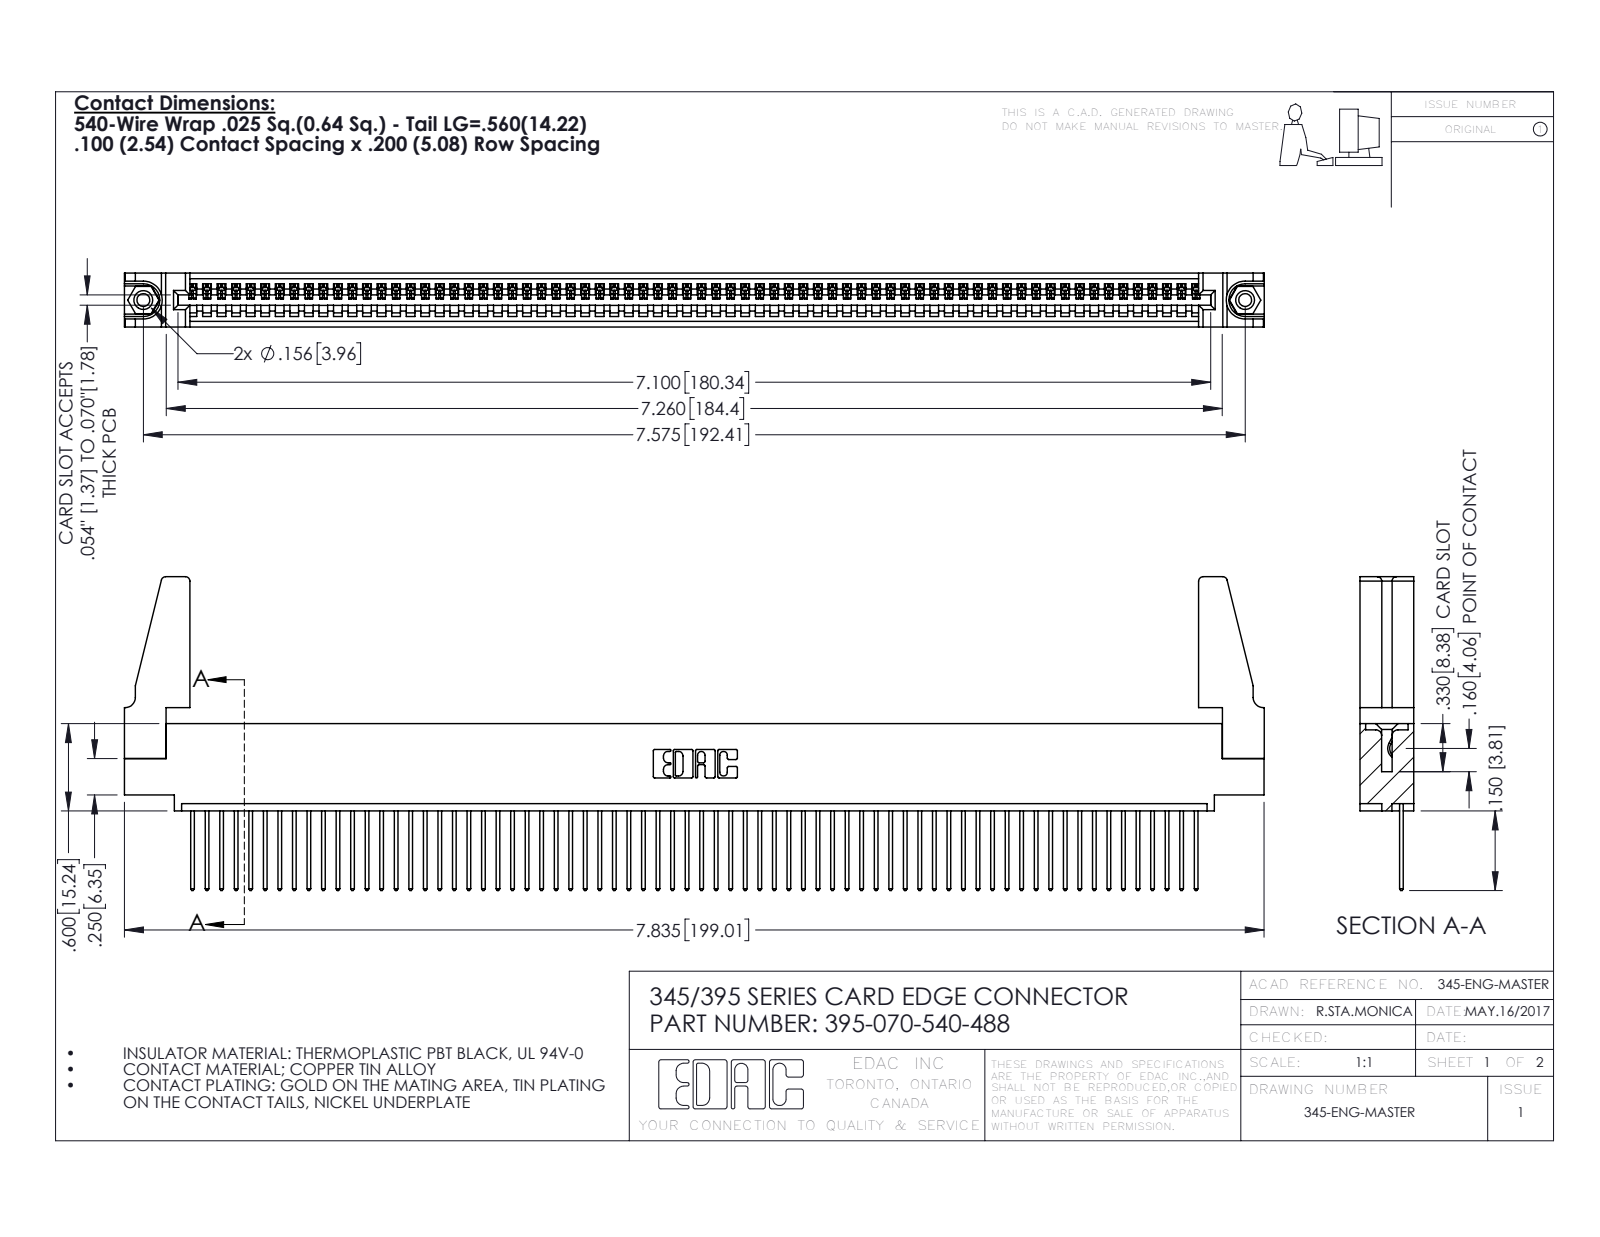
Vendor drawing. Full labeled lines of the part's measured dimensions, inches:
Part name (STEP PRODUCT): 345 Part_0.110 Offset - 0.156 Dia-TH; 345-220-078_345-220-088; 345-250-001_345-250-001-102; 345-292-001_345-293-140 (+1 more)
STEP written by: SolidWorks 2016 (CONFIG_CONTROL_DESIGN)
Units: inches
Bodies: 75 solids, 4314 faces (2956 planar, 1342 cylindrical, 16 other)
Overall size (bounding box): 7.836 × 2.157 × 0.37
Volume: 1.367 in³ · Surface area: 46.08 in²
Round holes (diameter × count): ⌀0.089 ×2, ⌀0.125 ×2, ⌀0.156 ×2, ⌀0.064 ×1
Round bosses / shafts (diameter × count): ⌀0.155 ×2
Partial cylindrical surfaces — rounded edges, fillets, slot ends (radius × count): R0.006 ×140, R0.01 ×140, R0.01 ×22, R0.03 ×8, R0.007 ×6, R0.031 ×6, R0.026 ×3, R0.031 ×2
Main face-to-face distances: 0.072, 0.298, 0.37, 0.098, 0.272, 0.025, 0.2, 0.225, 0.149, 0.072
Hole centre spacings: 0.27, 7.339, 7.575
